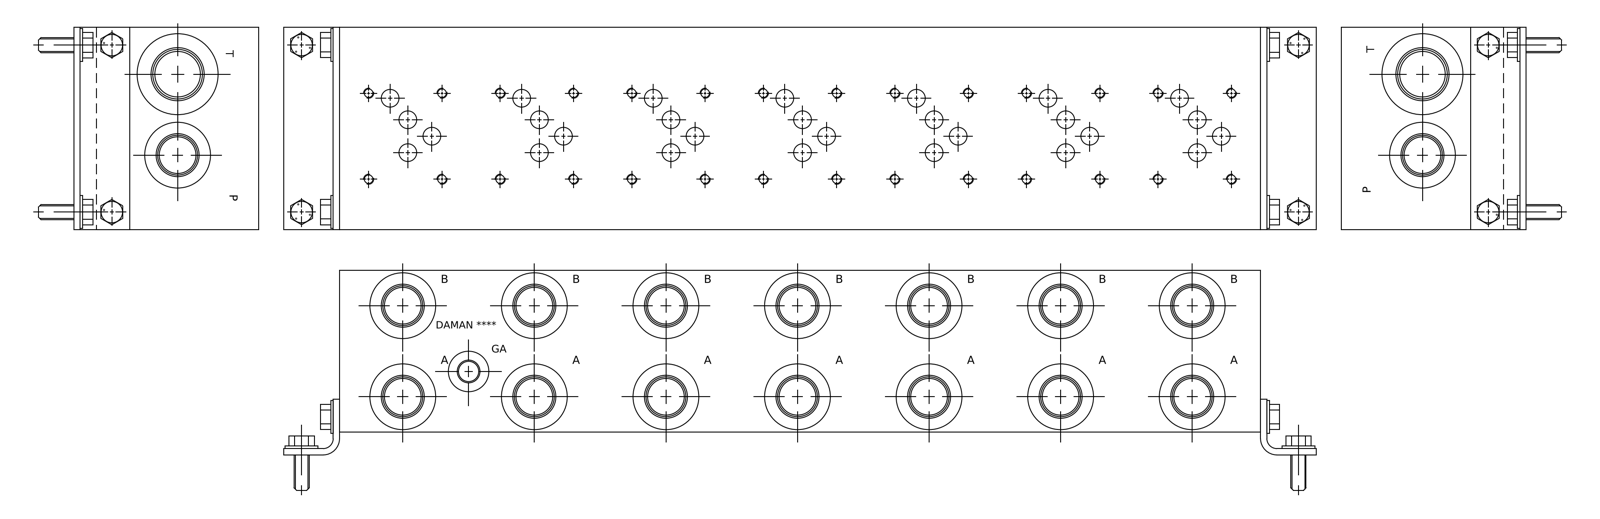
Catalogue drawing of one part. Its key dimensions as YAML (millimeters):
part_name: "Part_AD05HP073S_3D"
step_written_by: "Autodesk Inventor 2020 (AUTOMOTIVE_DESIGN)"
units: millimeters
bodies: {solids: 1, faces: 1086, planar: 536, cylindrical: 188, other: 362}
overall_size: [577.85, 127, 101.6]
volume: 7067000
surface_area: 357507
round_holes:
  - {diameter: 5.11, count: 28}
  - {diameter: 6.35, count: 28}
  - {diameter: 11.13, count: 26}
  - {diameter: 23.01, count: 15}
  - {diameter: 24.92, count: 15}
  - {diameter: 27.43, count: 15}
  - {diameter: 42.04, count: 15}
  - {diameter: 27, count: 14}
  - {diameter: 7.92, count: 2}
  - {diameter: 9.53, count: 2}
  - {diameter: 11.11, count: 2}
  - {diameter: 26.99, count: 2}
face_to_face_distances: [101.6, 127, 0.79, 126.21, 577.85, 577.06, 19.05, 576.27, 19.84, 107.16]
hole_center_spacings: [82.55, 165.1, 247.65, 330.2, 18.27, 68.25, 100.4, 85.09]
